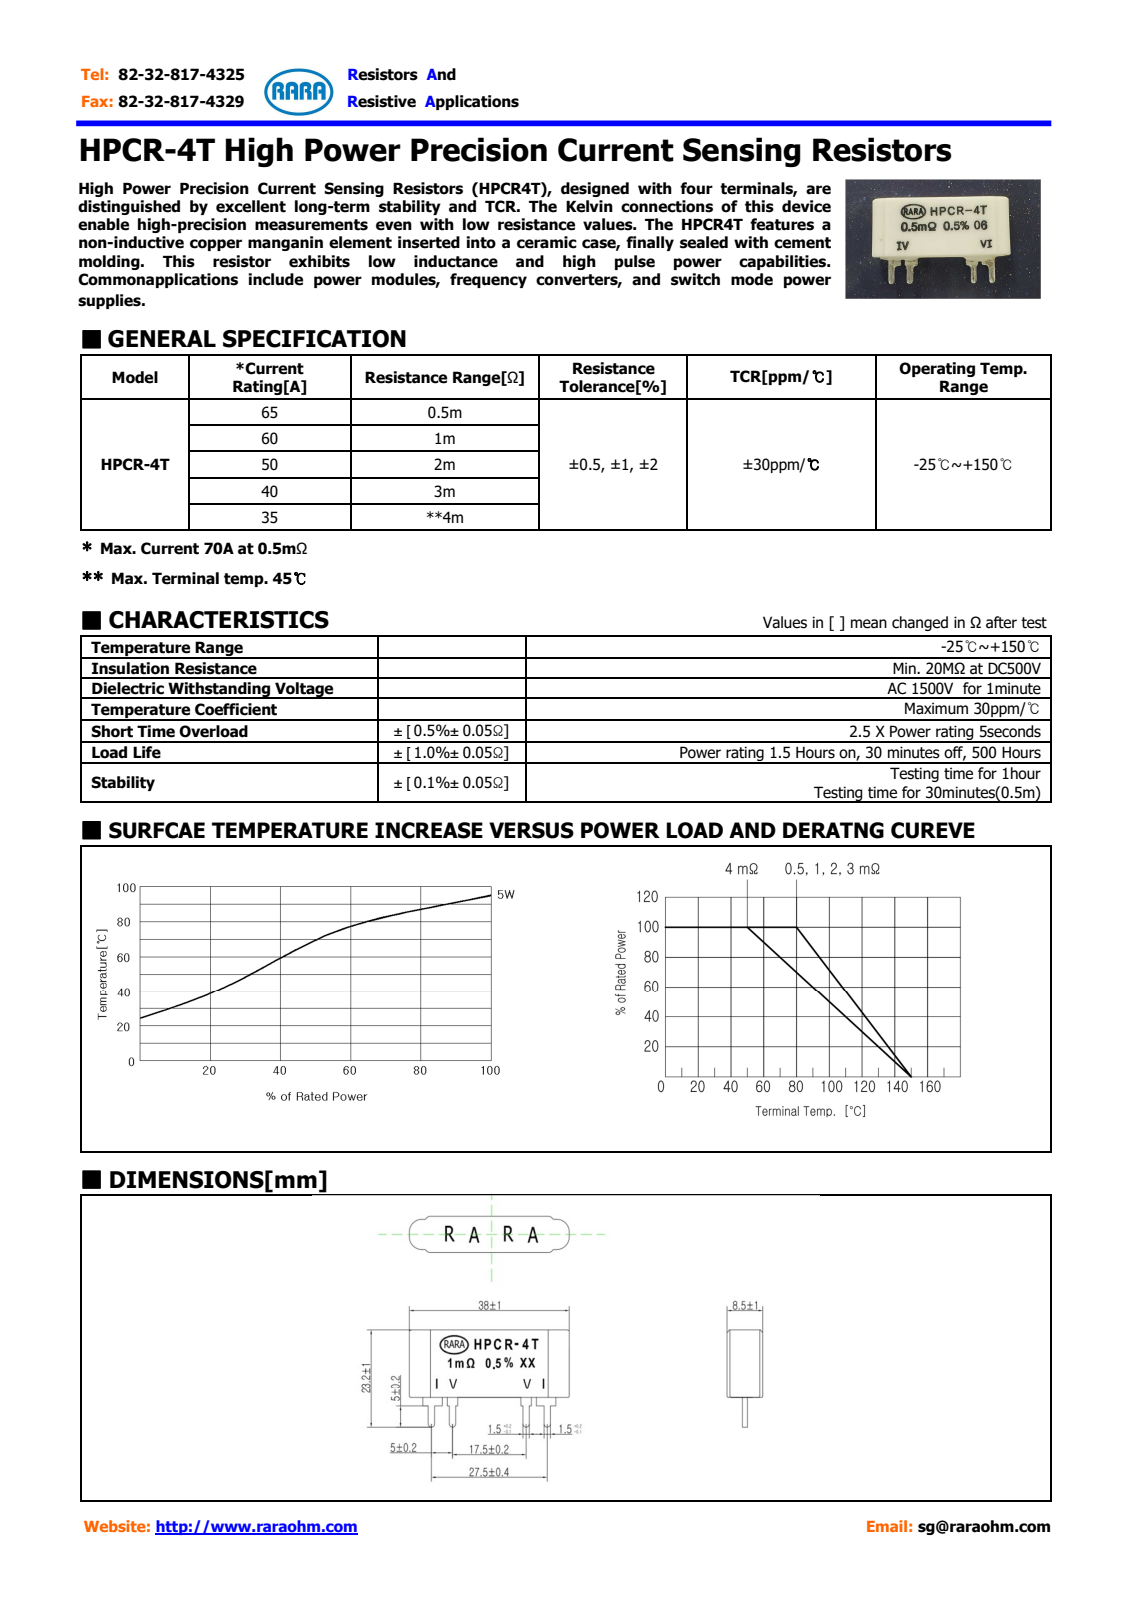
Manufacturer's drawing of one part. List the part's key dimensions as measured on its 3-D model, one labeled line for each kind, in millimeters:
Part name (STEP PRODUCT): HPCR4T 0.5m(1); HPCR4T (2)
STEP written by: SolidWorks 2018 (CONFIG_CONTROL_DESIGN)
Units: millimetres
Bodies: 5 solids, 145 faces (107 planar, 24 cylindrical, 14 other)
Overall size (bounding box): 38 × 23.6 × 8.5
Volume: 4 960 mm³ · Surface area: 2 357 mm²
Partial cylindrical surfaces — rounded edges, fillets, slot ends (radius × count): R0.5 ×8, R0.75 ×4, R1 ×4, R3 ×4
Main face-to-face distances: 8.5, 16.2, 1, 3.75, 4.75, 15.2, 0.5, 3.25, 8, 4.25
